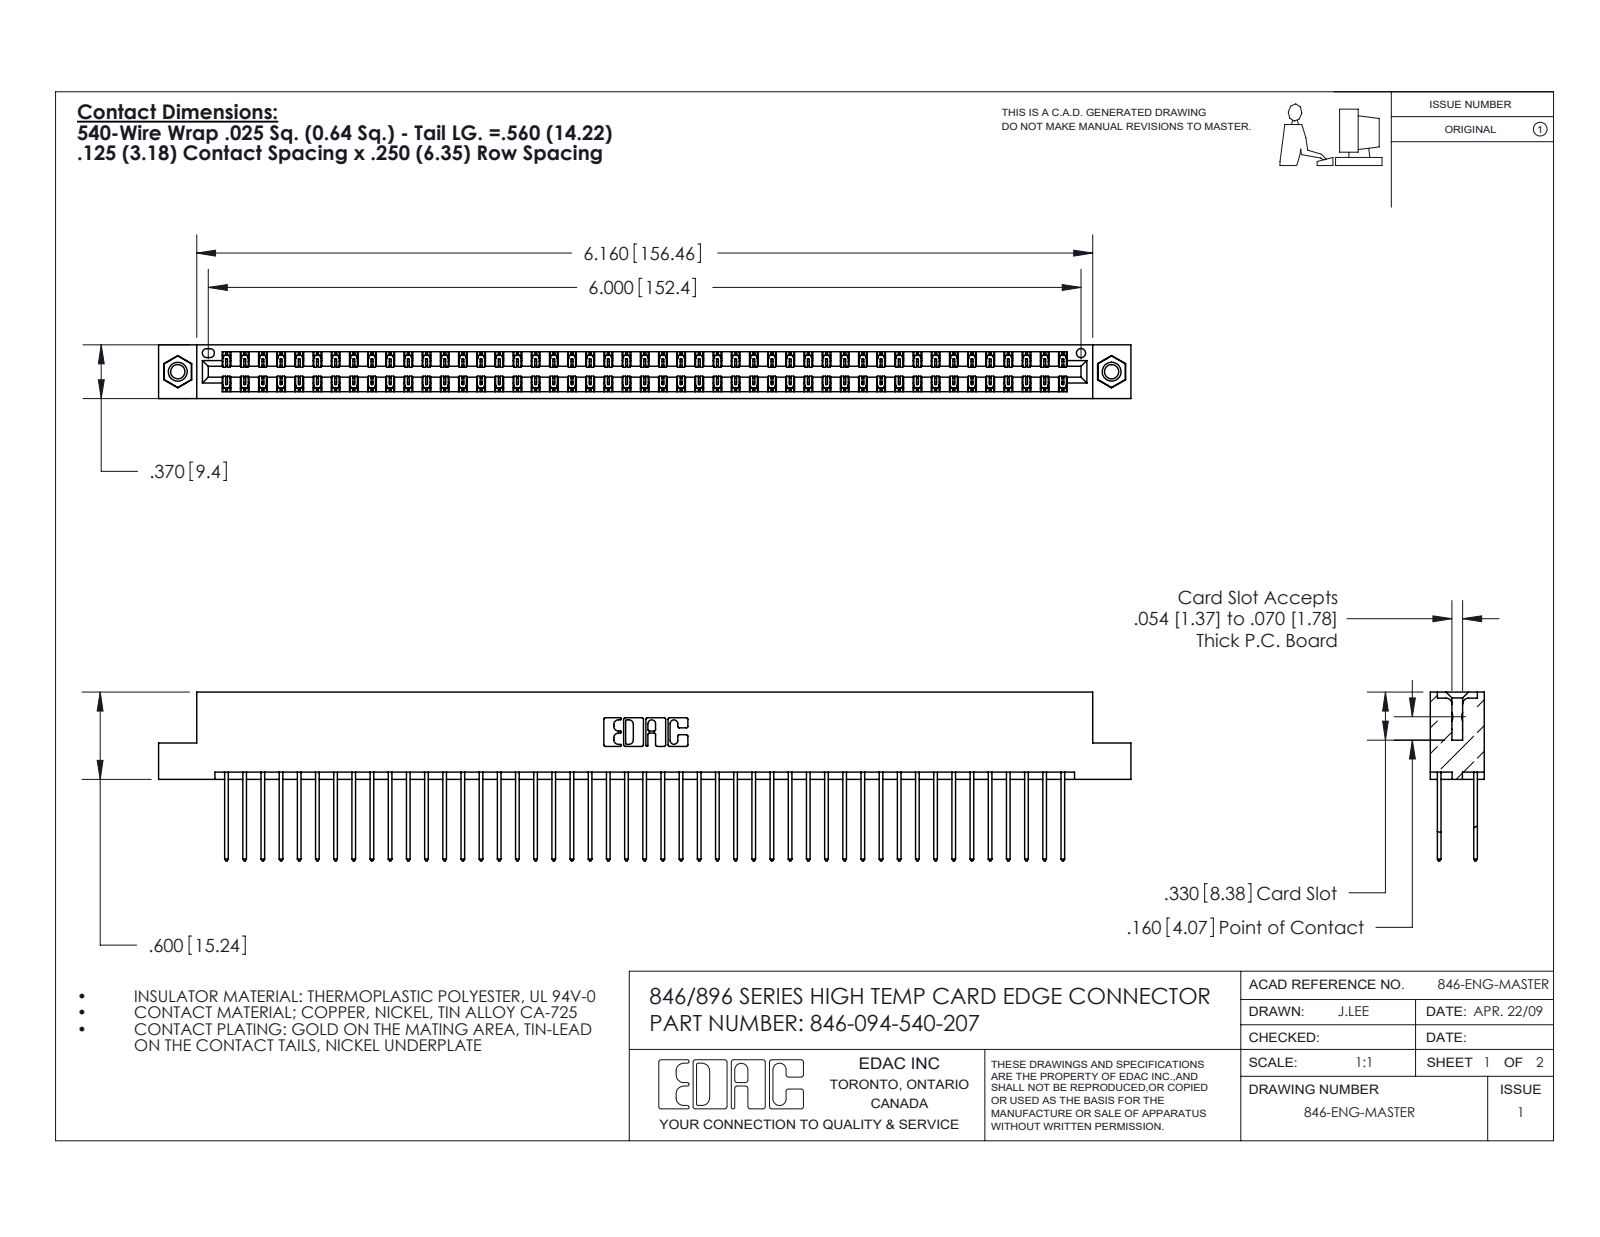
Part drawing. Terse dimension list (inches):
name: 346-094-540-207; 345-292-001_345-293-140; 346 Part_Flush Mounting Lugs - 0.156 Dia-TI; 345-250-001_345-250-005-103
written by: SolidWorks 2016 (CONFIG_CONTROL_DESIGN)
unit: in
bodies: 97 solids, 5070 faces (3398 planar, 1656 cylindrical, 16 other)
size: 6.685 × 1.16 × 0.37
volume: 1.034 in³; area: 38.88 in²
holes: 2× ⌀0.098, 2× ⌀0.125, 2× ⌀0.156, 1× ⌀0.064
bosses: 2× ⌀0.155
rounds: 141× R0.006, 94× R0.01, 22× R0.01, 6× R0.007, 6× R0.031, 3× R0.026, 2× R0.014, 2× R0.022
face distances: 0.048, 0.322, 0.25, 0.072, 0.298, 0.025, 0.37, 0.275, 0.148, 0.222
hole spacings: 0.246, 6.211, 6.42
